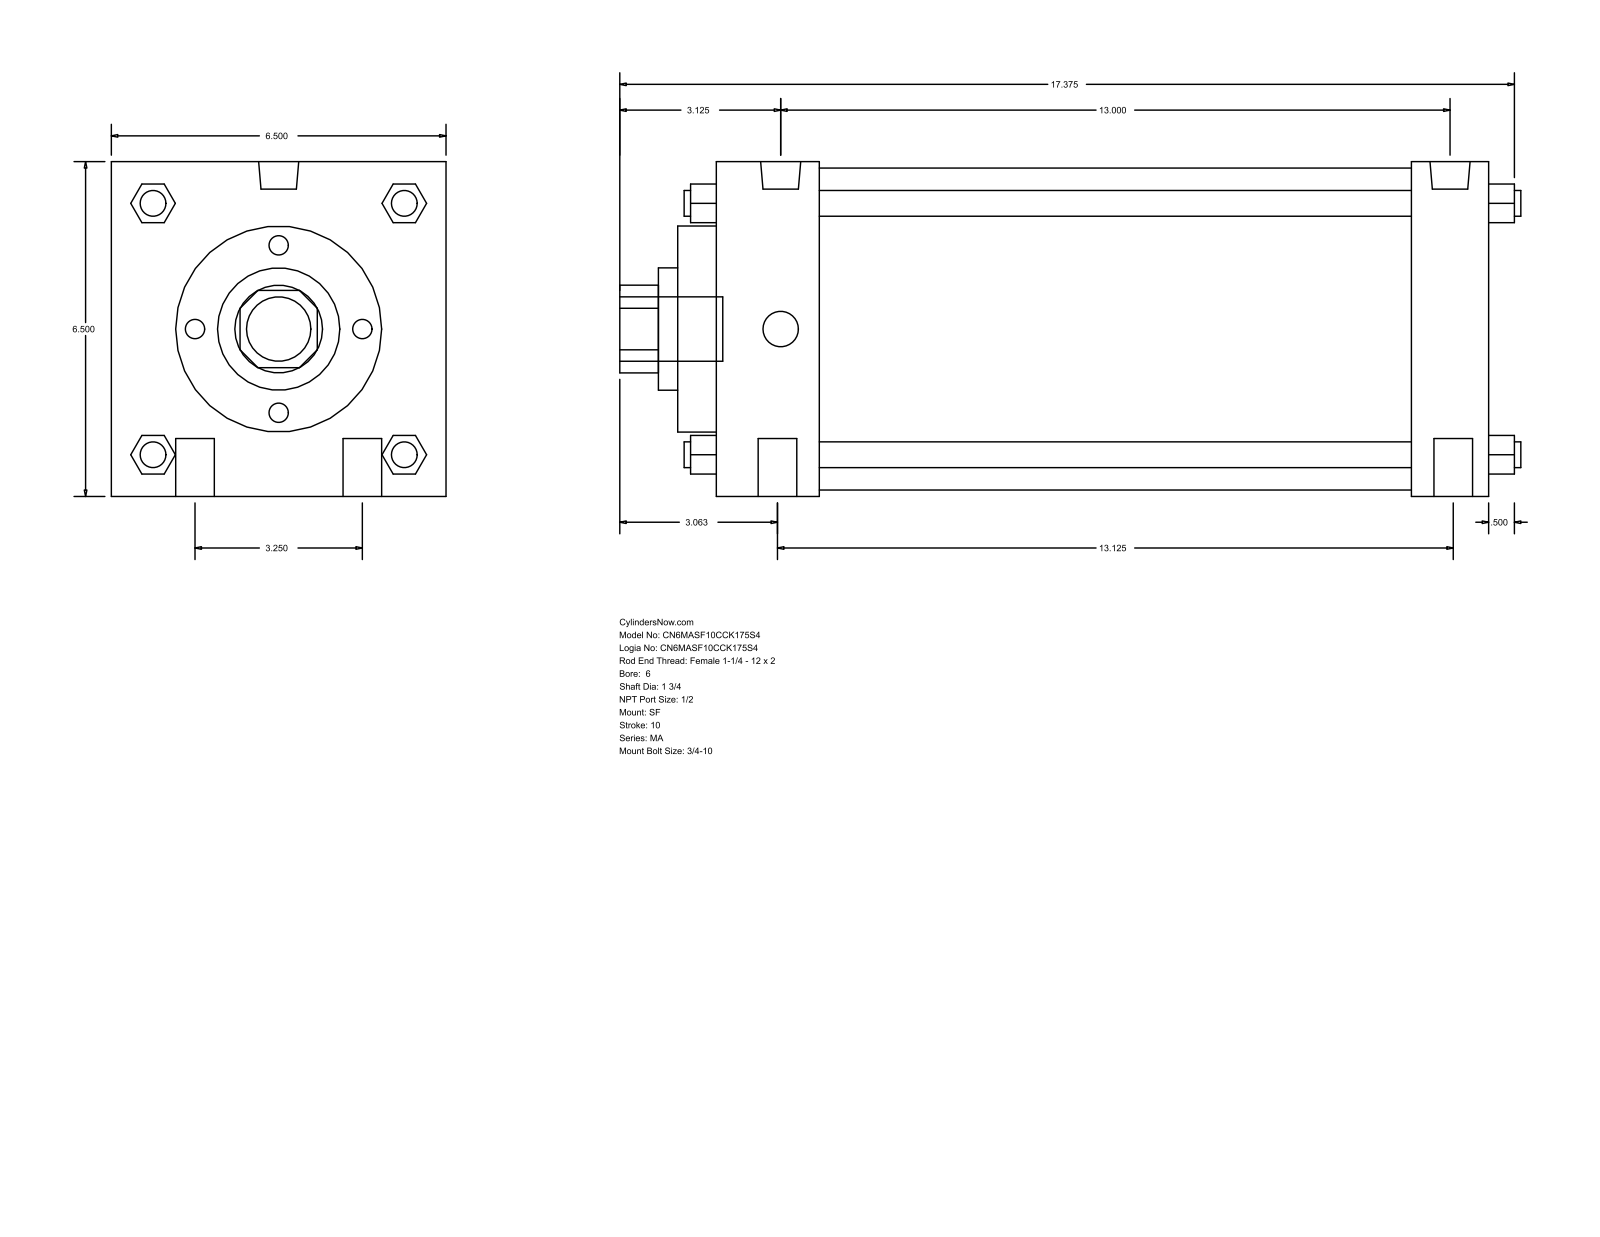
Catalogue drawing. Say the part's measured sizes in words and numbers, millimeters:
The part is named "MA_SF__0600_1.75". Its 3-D file was written by "GSSL Pune (CONFIG_CONTROL_DESIGN)". It is 0 solids with 126 faces: 95 planar, 31 cylindrical and 0 other. Overall it measures 444.5 by 165.1 by 165.1 millimeters. Round holes: 1 of diameter 44.45, 1 of diameter 60.33, 1 of diameter 101.6, 1 of diameter 158.75. Round bosses or shafts: 4 of diameter 19.05, 4 of diameter 12.7, 2 of diameter 19.77, 2 of diameter 17.46, 1 of diameter 31.75. Partial cylindrical surfaces (rounded edges, fillets, slot ends): 1 of radius 21.63. The main face-to-face distances are 165.1, 381, 19.05, 50.8, 342.9, 38.1, 292.1, 330.2, 69.85, 361.95.
